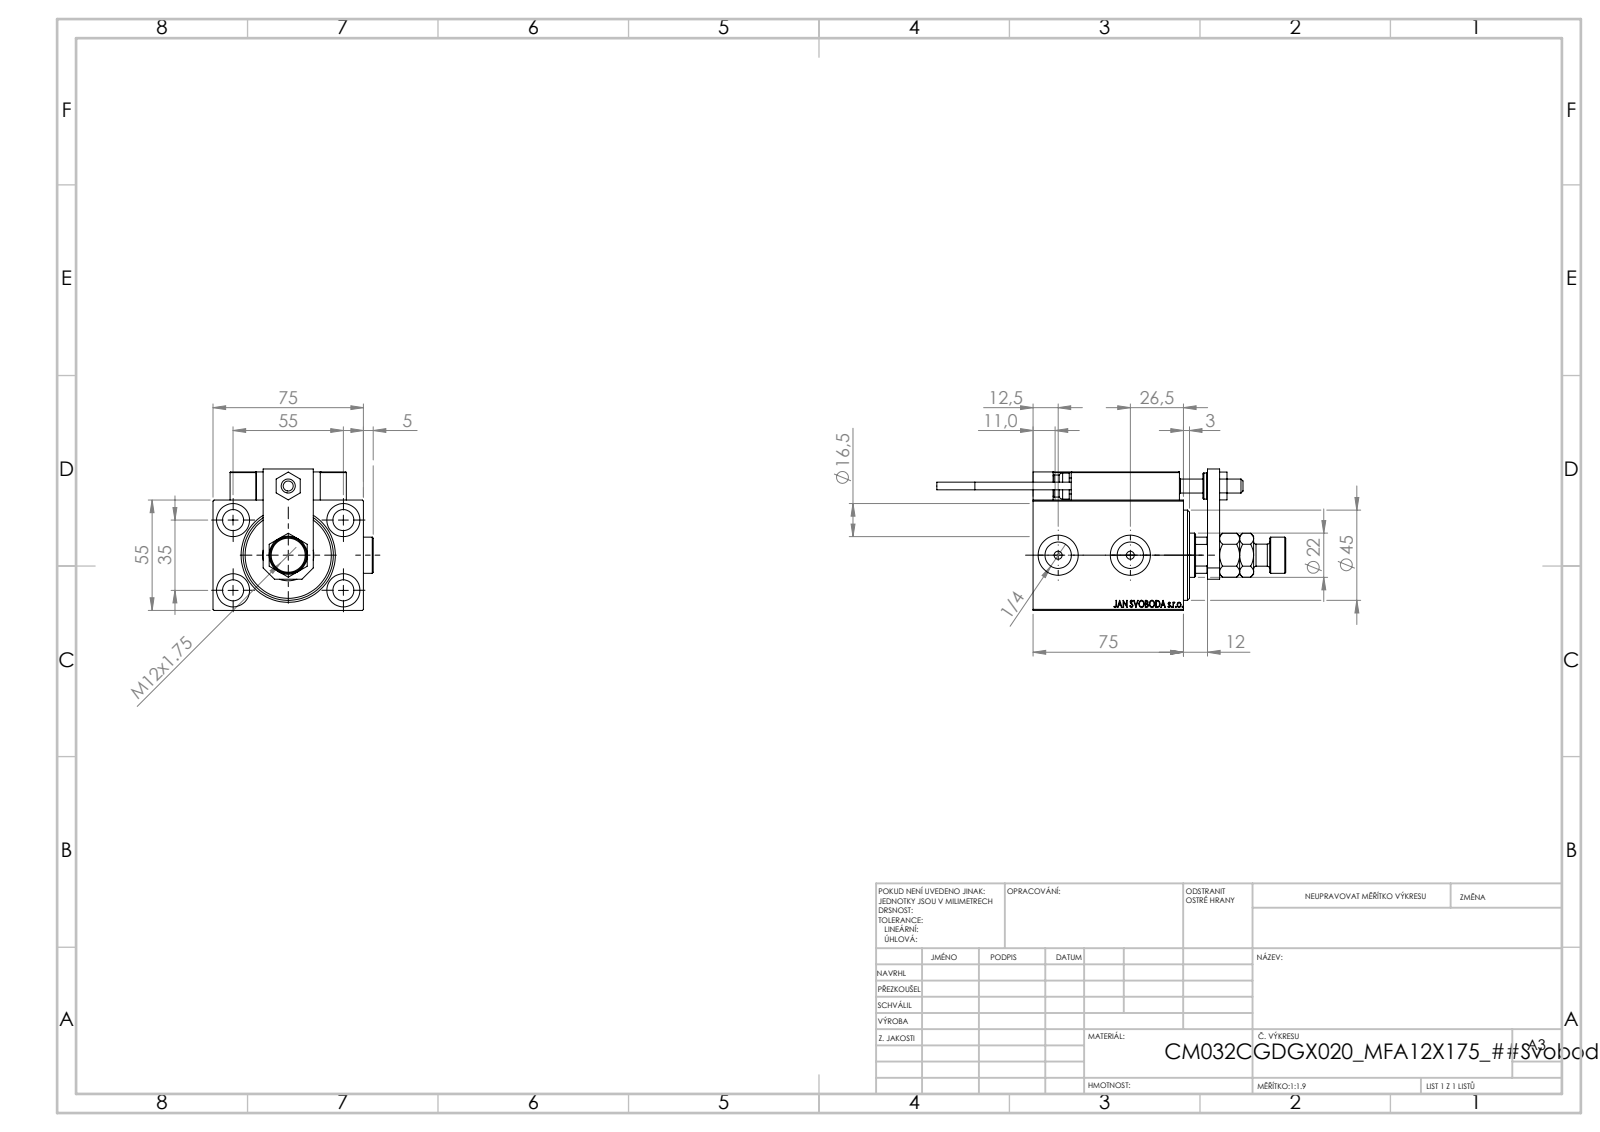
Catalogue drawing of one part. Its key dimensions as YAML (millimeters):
part_name: "SWITCH_X_FRONT_BACK; KONCOVKA; TYC_L79; ALLEN BOLT D5 (+7 more)"
step_written_by: "SolidWorks 2019 (CONFIG_CONTROL_DESIGN)"
units: millimeters
bodies: {solids: 26, faces: 1388, planar: 610, cylindrical: 208, other: 570}
overall_size: [174, 79.9, 70.5]
volume: 319764
surface_area: 90118
round_holes:
  - {diameter: 4, count: 6}
  - {diameter: 8, count: 5}
  - {diameter: 10.5, count: 5}
  - {diameter: 16.5, count: 5}
  - {diameter: 3.2, count: 4}
  - {diameter: 5, count: 2}
  - {diameter: 13.16, count: 2}
  - {diameter: 20, count: 2}
  - {diameter: 7, count: 1}
  - {diameter: 22, count: 1}
  - {diameter: 25.5, count: 1}
  - {diameter: 32, count: 1}
round_bosses_or_shafts:
  - {diameter: 18, count: 3}
  - {diameter: 11, count: 2}
  - {diameter: 5, count: 2}
  - {diameter: 3.8, count: 2}
  - {diameter: 13, count: 1}
partial_cylinders:
  - {radius: 0.3, count: 30}
  - {radius: 3, count: 2}
  - {radius: 10.5, count: 1}
face_to_face_distances: [55, 75, 14, 10, 12, 5, 7, 3, 69, 15]
hole_center_spacings: [32.6, 11.37, 20, 27.07, 29.59, 29.69, 32.33, 34.83]
